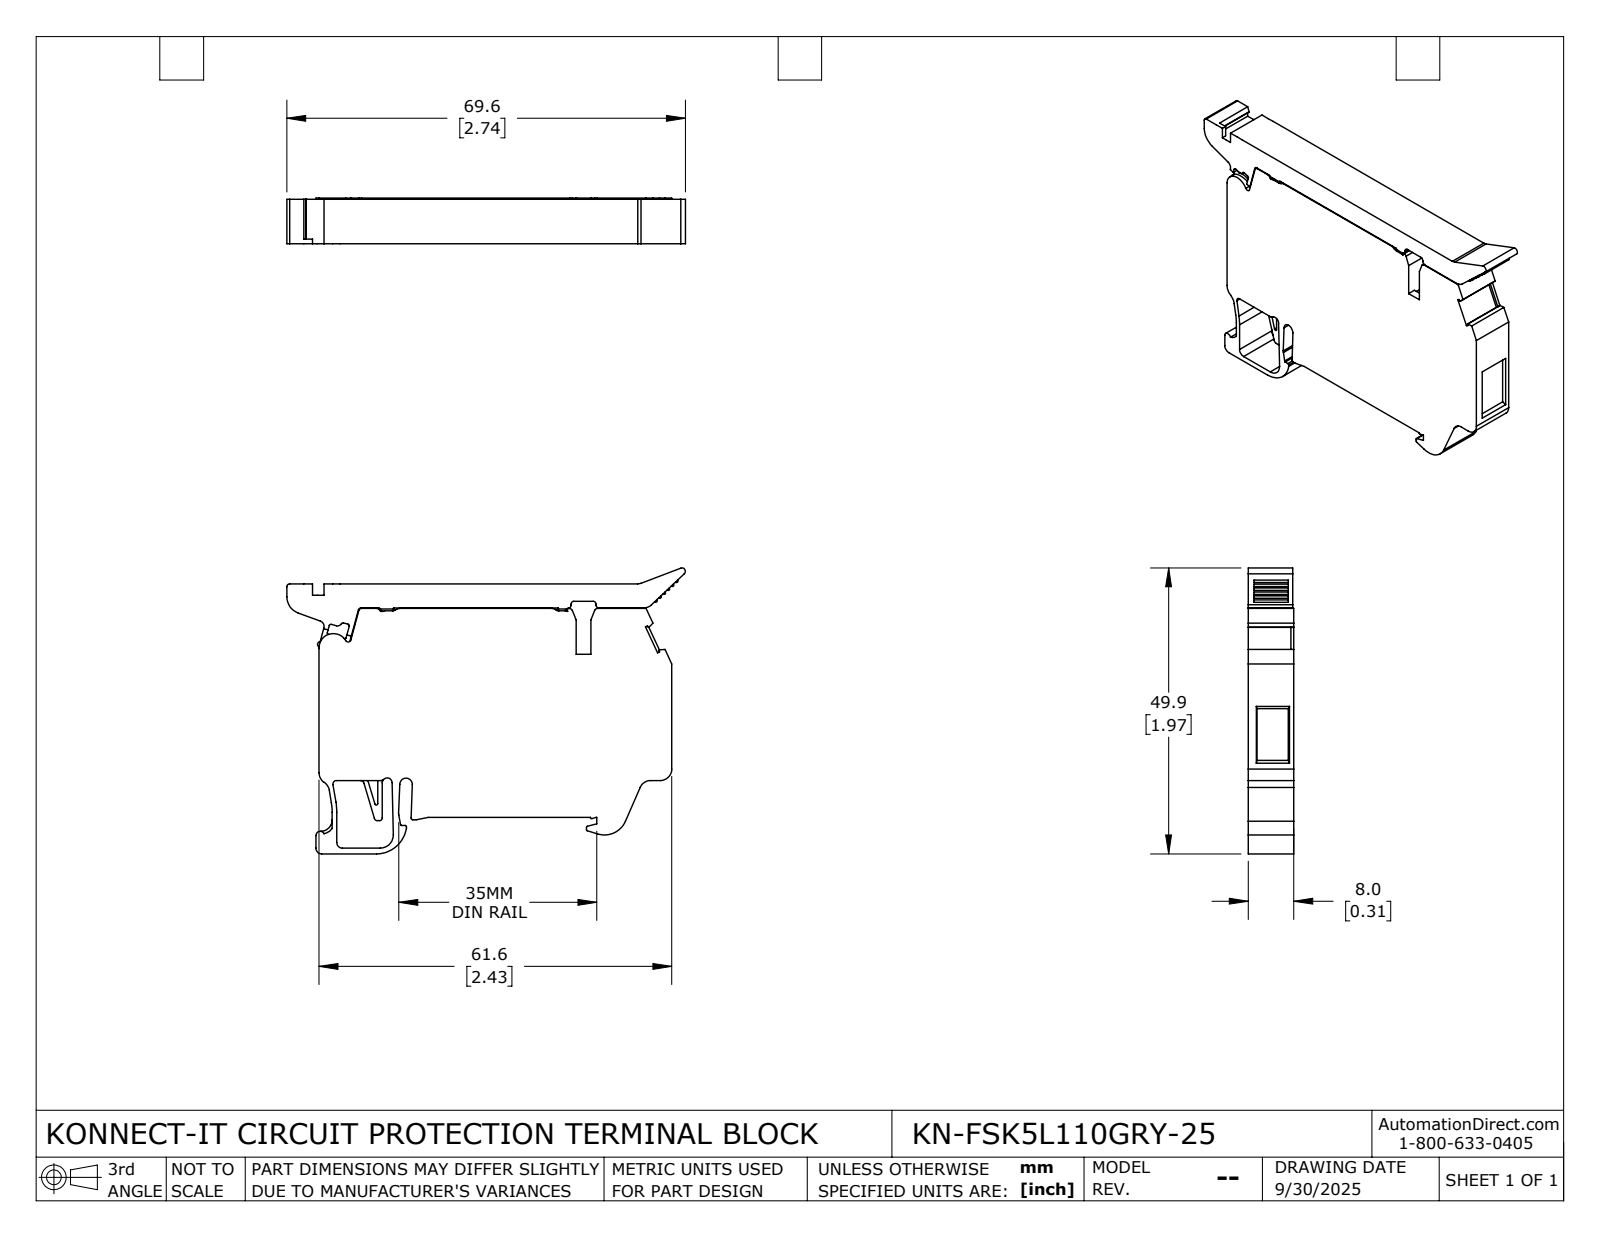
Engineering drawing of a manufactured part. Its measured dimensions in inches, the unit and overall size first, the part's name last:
Units: inches
Overall size (bounding box): 2.74 × 1.965 × 0.313
Round holes (diameter × count): ⌀0.197 ×1
Partial cylindrical surfaces — rounded edges, fillets, slot ends (radius × count): R0.02 ×16, R0.039 ×10, R0.012 ×8, R0.079 ×8, R0.008 ×7, R0.01 ×7, R0.004 ×4, R0.098 ×3
Main face-to-face distances: 0.313, 0.305, 0.165, 0.024, 0.02, 1.44, 1.606, 0.189, 1.417, 2.406
Volume: 1.146 in³ · Surface area: 13.11 in²
Bodies: 1 solid, 318 faces (181 planar, 124 cylindrical, 13 other)
Part name (STEP PRODUCT): KN-FSK5L110GRY-25
STEP written by: SolidWorks 2024 (CONFIG_CONTROL_DESIGN)
